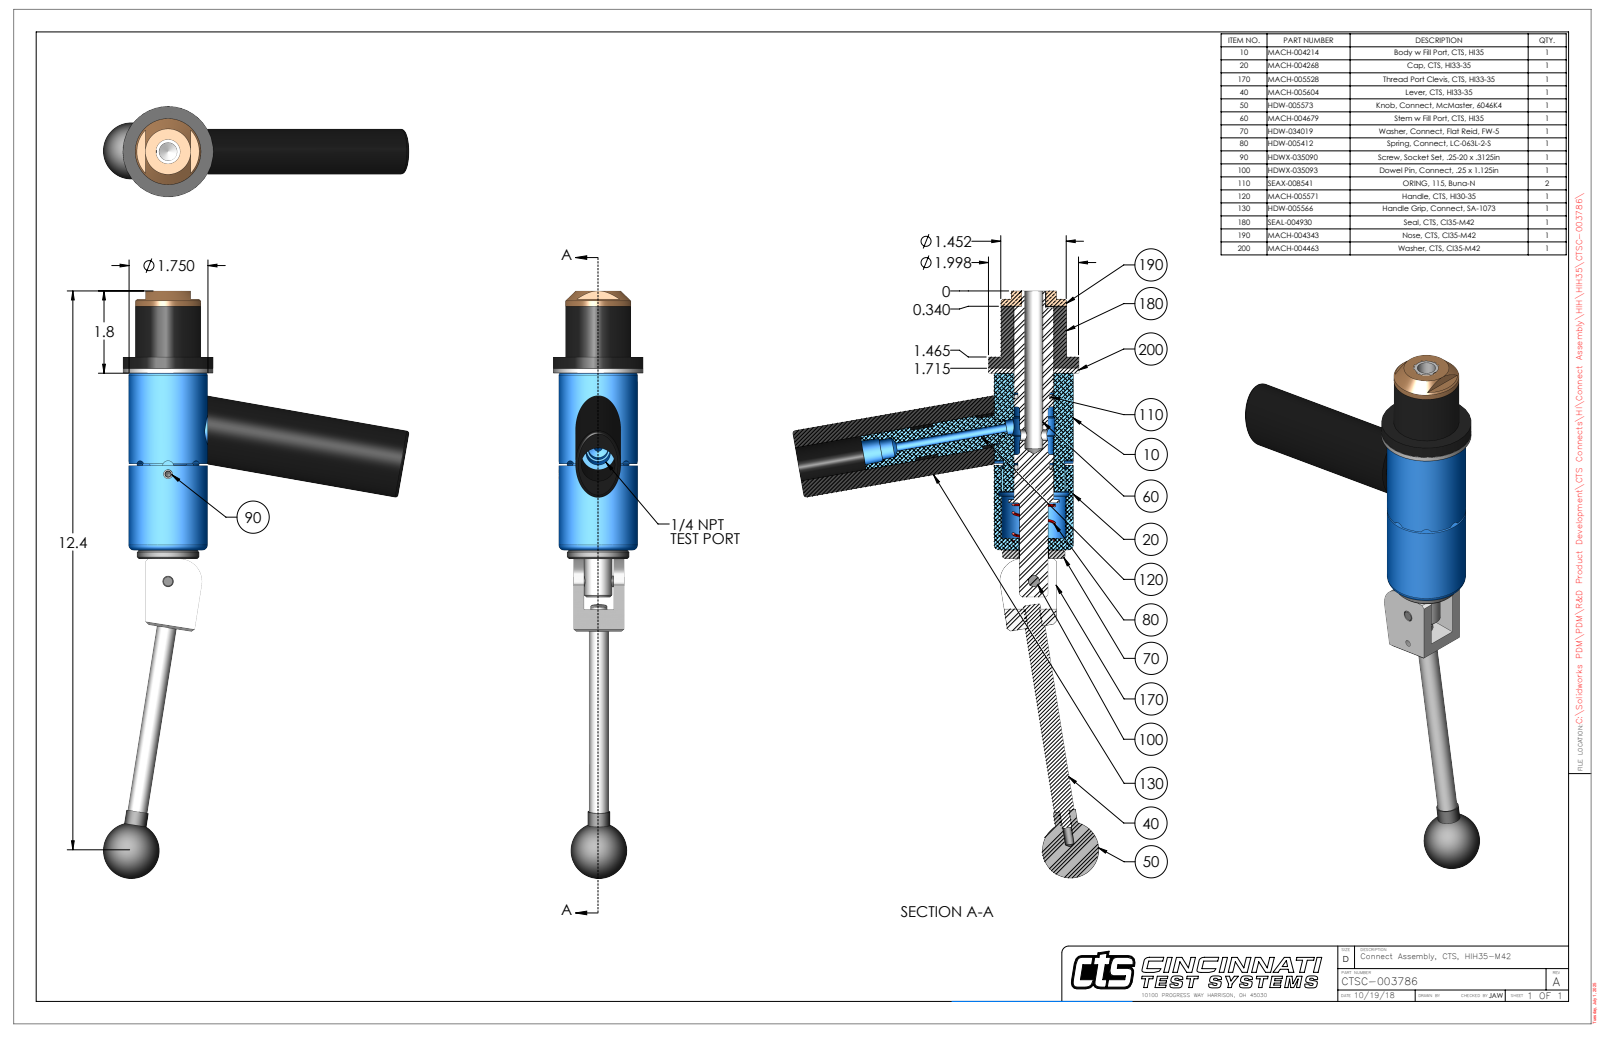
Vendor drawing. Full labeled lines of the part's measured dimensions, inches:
Part name (STEP PRODUCT): CTSC-003786
STEP written by: SolidWorks 2023 (AUTOMOTIVE_DESIGN)
Units: inches
Bodies: 11 solids, 298 faces (107 planar, 124 cylindrical, 67 other)
Overall size (bounding box): 13.02 × 6.763 × 1.998
Volume: 19.97 in³ · Surface area: 133.8 in²
Round holes (diameter × count): ⌀0.201 ×2, ⌀0.15 ×1, ⌀0.187 ×1, ⌀0.249 ×1, ⌀0.25 ×1, ⌀0.251 ×1, ⌀0.313 ×1, ⌀0.406 ×1, ⌀0.438 ×1, ⌀0.531 ×1, ⌀0.635 ×1, ⌀0.656 ×1
Round bosses / shafts (diameter × count): ⌀0.25 ×2, ⌀1.998 ×1, ⌀1.998 ×1, ⌀1.75 ×1, ⌀1.452 ×1, ⌀1.452 ×1, ⌀1.38 ×1, ⌀0.869 ×1
Partial cylindrical surfaces — rounded edges, fillets, slot ends (radius × count): R0.125 ×4, R0.029 ×2, R0.166 ×1, R0.166 ×1, R0.246 ×1, R0.33 ×1, R0.5 ×1, R0.695 ×1
Main face-to-face distances: 0.11, 1.375, 1.485, 5.405, 4.03, 3.92, 1.12, 0.25, 1.125, 0.36
Hole centre spacings: 0.74, 2.376, 3.116
